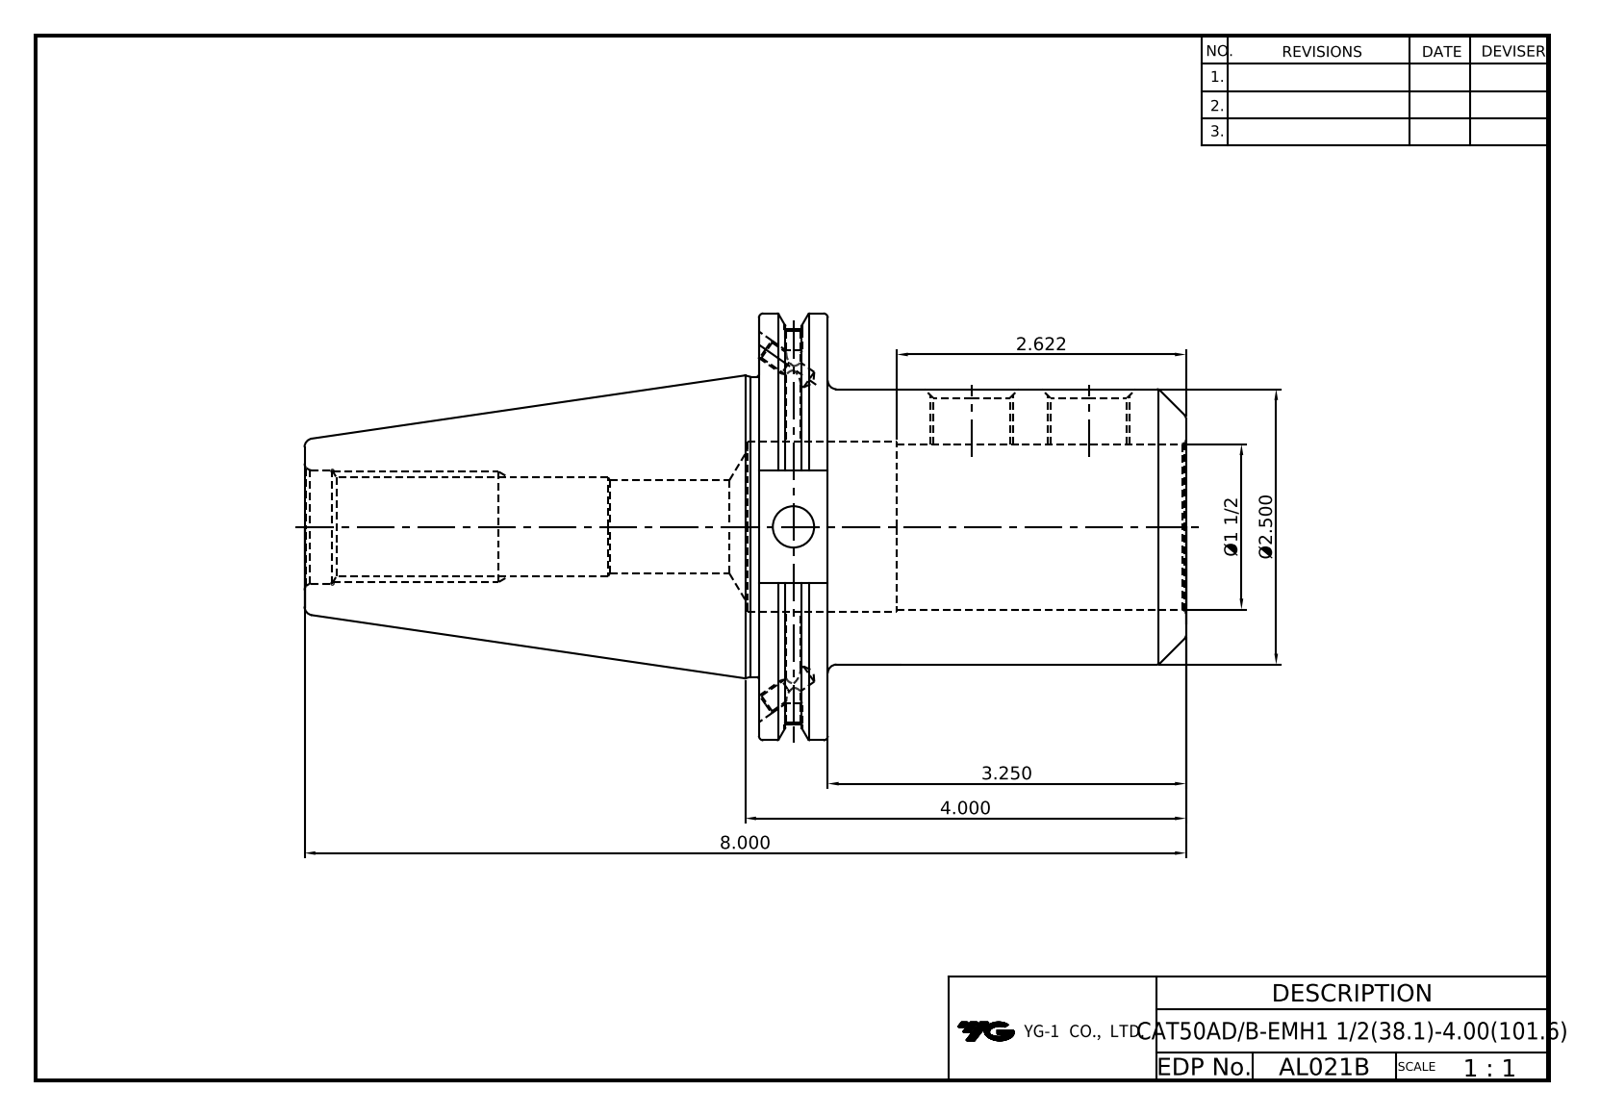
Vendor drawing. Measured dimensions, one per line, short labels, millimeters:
name: LO-CAT50ADB-EMH38.1-101.6
written by: Autodesk Inventor 2022 (AUTOMOTIVE_DESIGN)
unit: mm
bodies: 1 solid, 91 faces (39 planar, 28 cylindrical, 24 other)
size: 203.2 × 98.42 × 94.69
volume: 459 800 mm³; area: 71 323 mm²
holes: 2× ⌀3.24, 2× ⌀4.13, 2× ⌀4.2, 2× ⌀5, 2× ⌀17.32, 1× ⌀9.53, 1× ⌀21.5, 1× ⌀21.97, 1× ⌀26.2, 1× ⌀38.1, 1× ⌀39.3
bosses: 1× ⌀98.42, 1× ⌀91.29, 1× ⌀69.25, 1× ⌀63.5
face distances: 15.88, 2.57, 18.45, 101, 98.43, 82.55, 102.2, 104.77, 120.65, 203.2
hole spacings: 27
